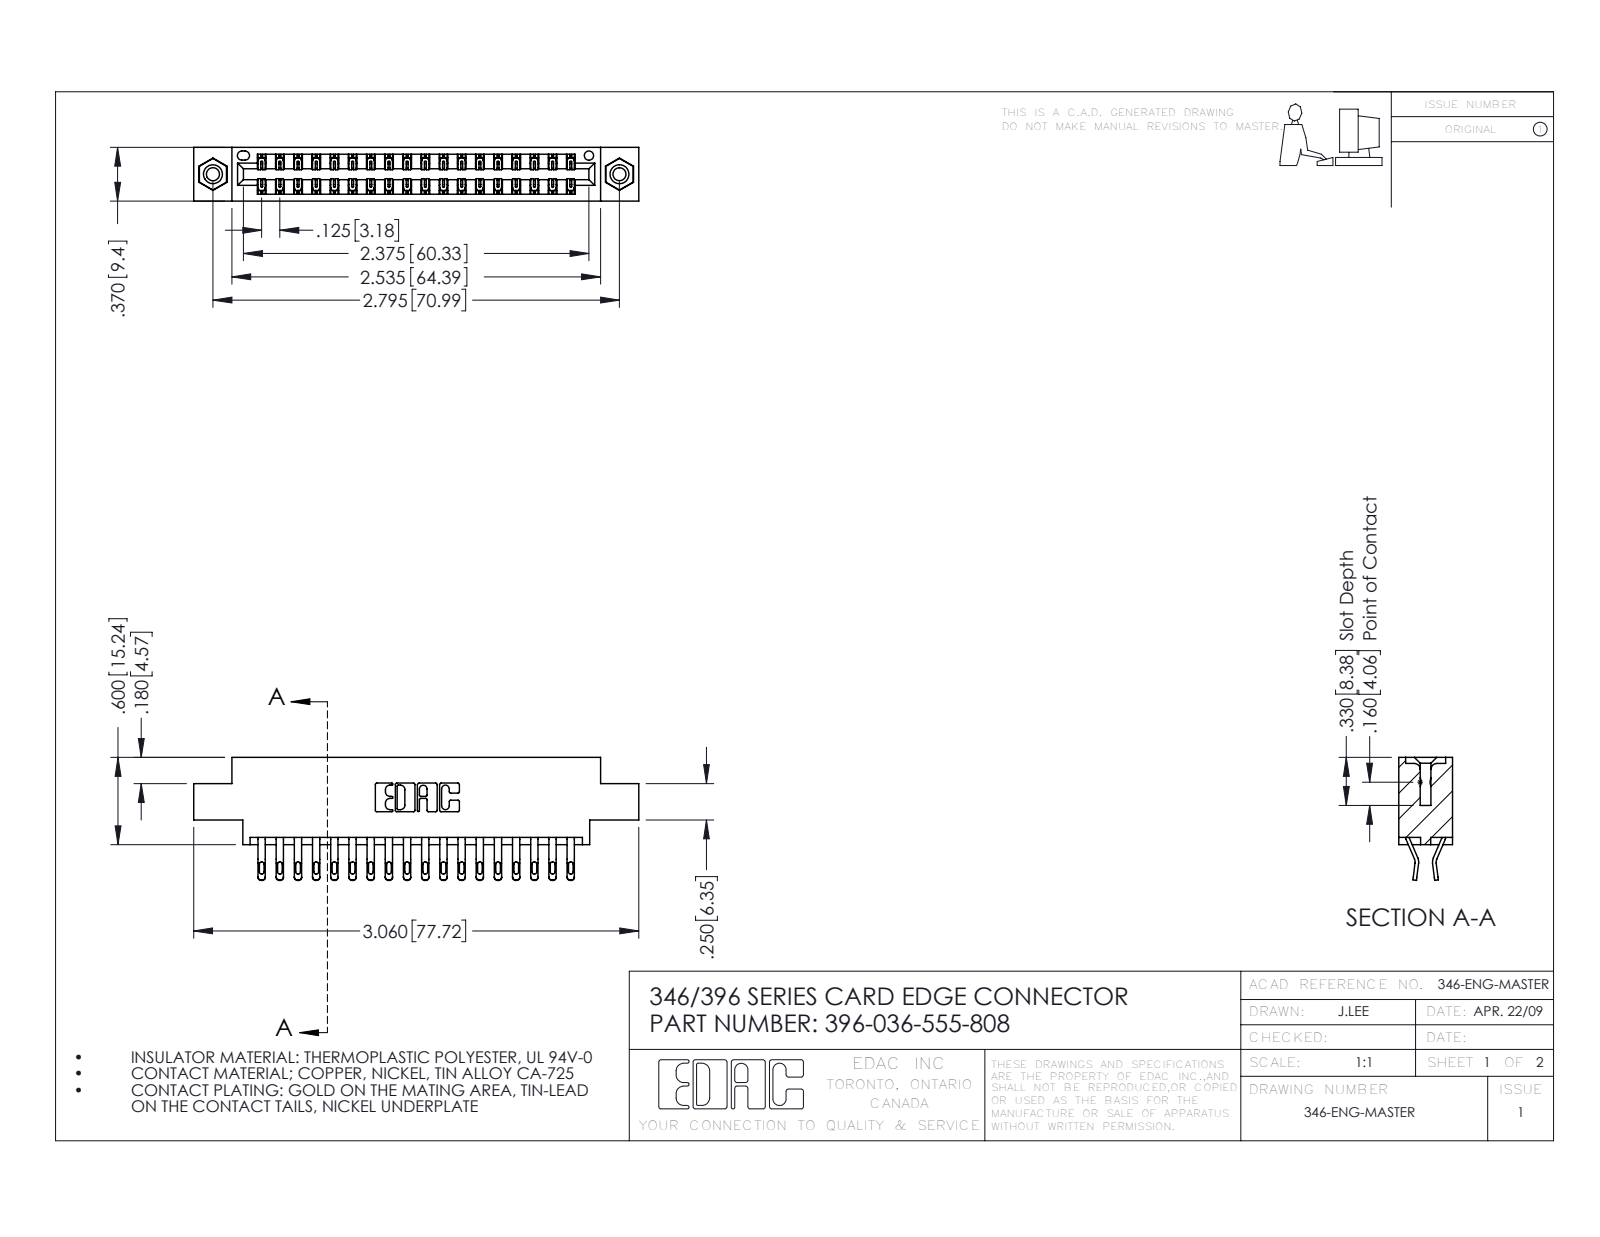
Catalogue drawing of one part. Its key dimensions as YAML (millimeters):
part_name: "345-250-001_345-250-003-102; 346 Part_0.170 Offset - 0.156 Dia-TI; 396-036-555-808; 345-292-001_555 Tail"
step_written_by: "SolidWorks 2016 (CONFIG_CONTROL_DESIGN)"
units: millimeters
bodies: {solids: 39, faces: 2274, planar: 1300, cylindrical: 958, other: 16}
overall_size: [77.7, 21.5, 9.4]
volume: 7340
surface_area: 10280
round_holes:
  - {diameter: 2.3, count: 2}
  - {diameter: 3.2, count: 2}
  - {diameter: 4, count: 2}
  - {diameter: 1.6, count: 1}
round_bosses_or_shafts:
  - {diameter: 3.9, count: 2}
partial_cylinders:
  - {radius: 0.4, count: 72}
  - {radius: 0.5, count: 72}
  - {radius: 0.2, count: 54}
  - {radius: 0.3, count: 22}
  - {radius: 0.2, count: 6}
  - {radius: 0.8, count: 6}
  - {radius: 0.7, count: 3}
  - {radius: 0.3, count: 2}
face_to_face_distances: [1.2, 8.2, 9.4, 6.4, 0.6, 1.8, 7.6, 7, 5.6, 3.8]
hole_center_spacings: [6.2, 65.7, 71]
